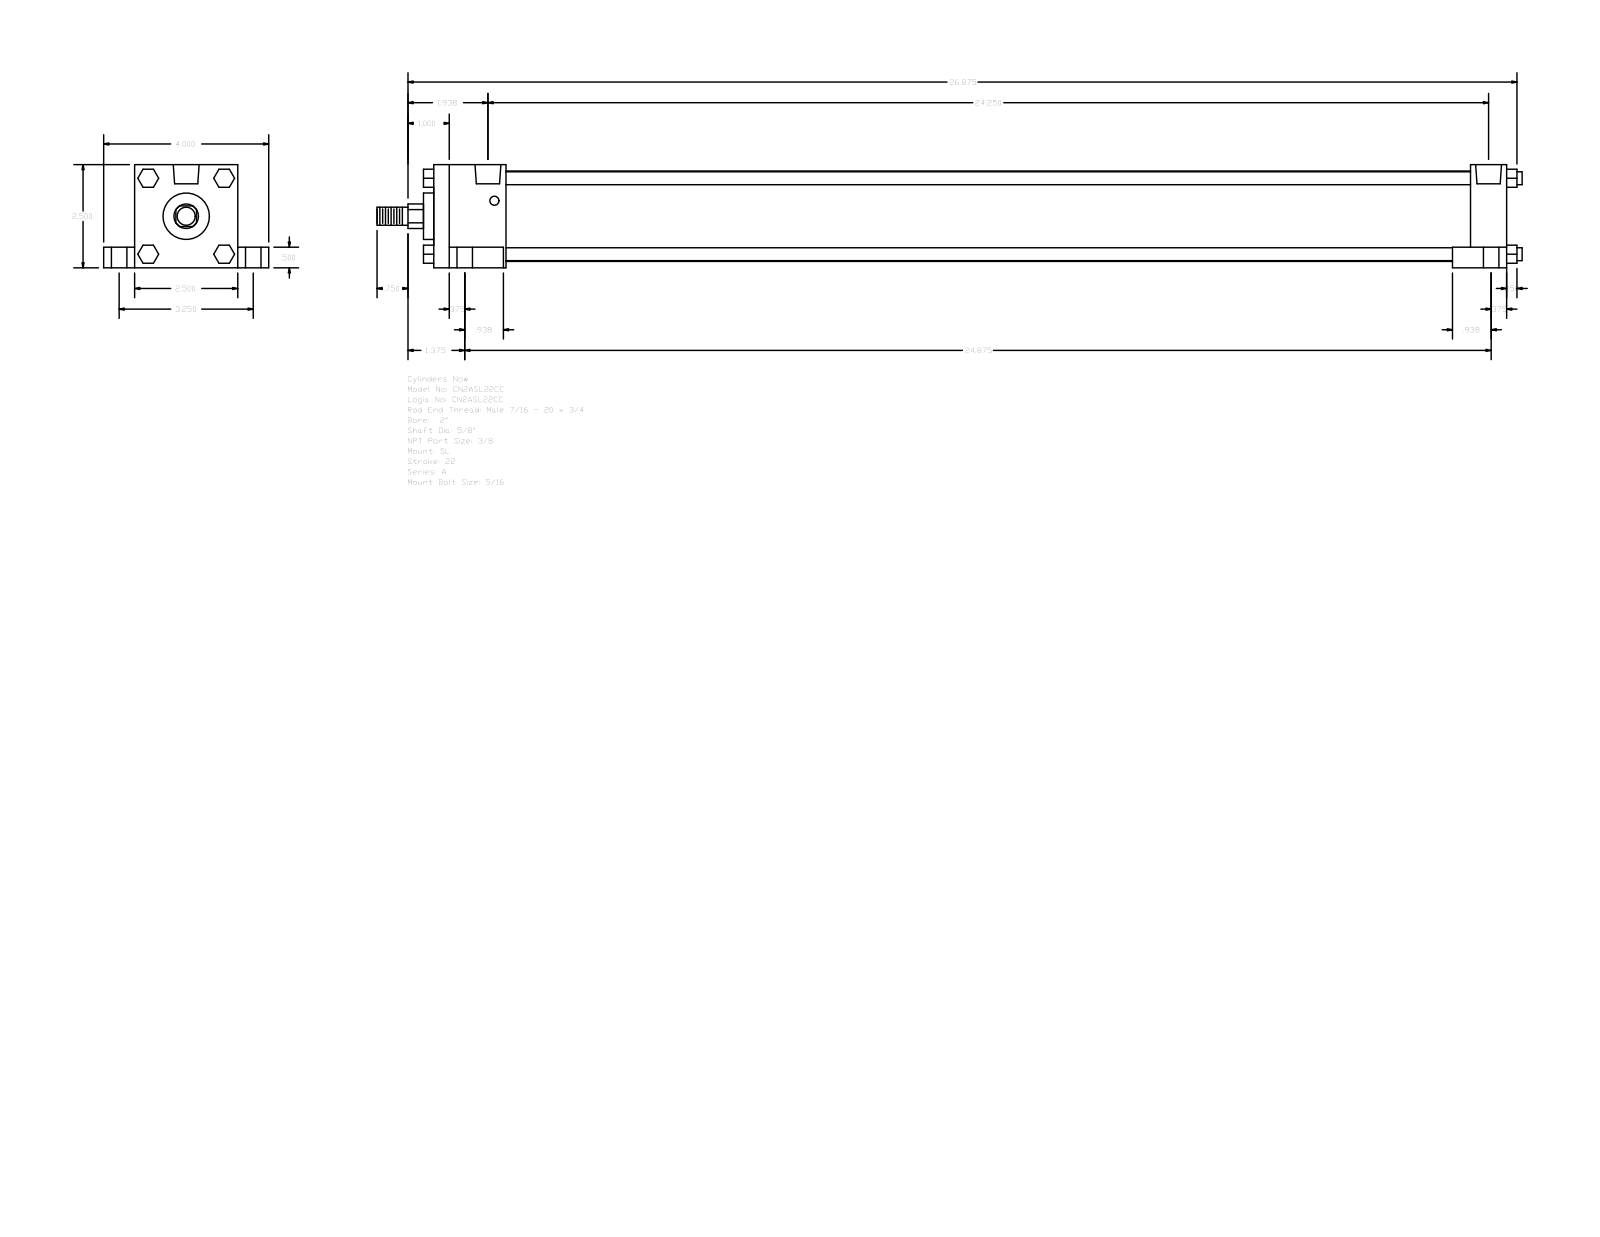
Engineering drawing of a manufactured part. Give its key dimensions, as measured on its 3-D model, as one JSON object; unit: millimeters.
{"part_name": "A_SL__0200_0.625", "step_written_by": "GSSL Pune (CONFIG_CONTROL_DESIGN)", "units": "millimeters", "bodies": {"solids": 0, "faces": 148, "planar": 112, "cylindrical": 36, "other": 0}, "overall_size": [704.85, 101.6, 63.5], "round_holes": [[5.56, 4], [9.53, 4], [15.88, 4], [15.93, 2]], "round_bosses_or_shafts": [[7.94, 4], [55.63, 1], [28.57, 1], [15.88, 1], [11.11, 1]], "partial_cylinders_radius": [[7.54, 1]], "face_to_face_distances": [63.5, 660.39, 50.8, 12.7, 19.05, 82.55, 44.45, 615.94, 638.17, 593.72], "hole_center_spacings": [41.3, 41.64, 43.67, 45.13, 82.54, 608, 614.95, 618.92]}
